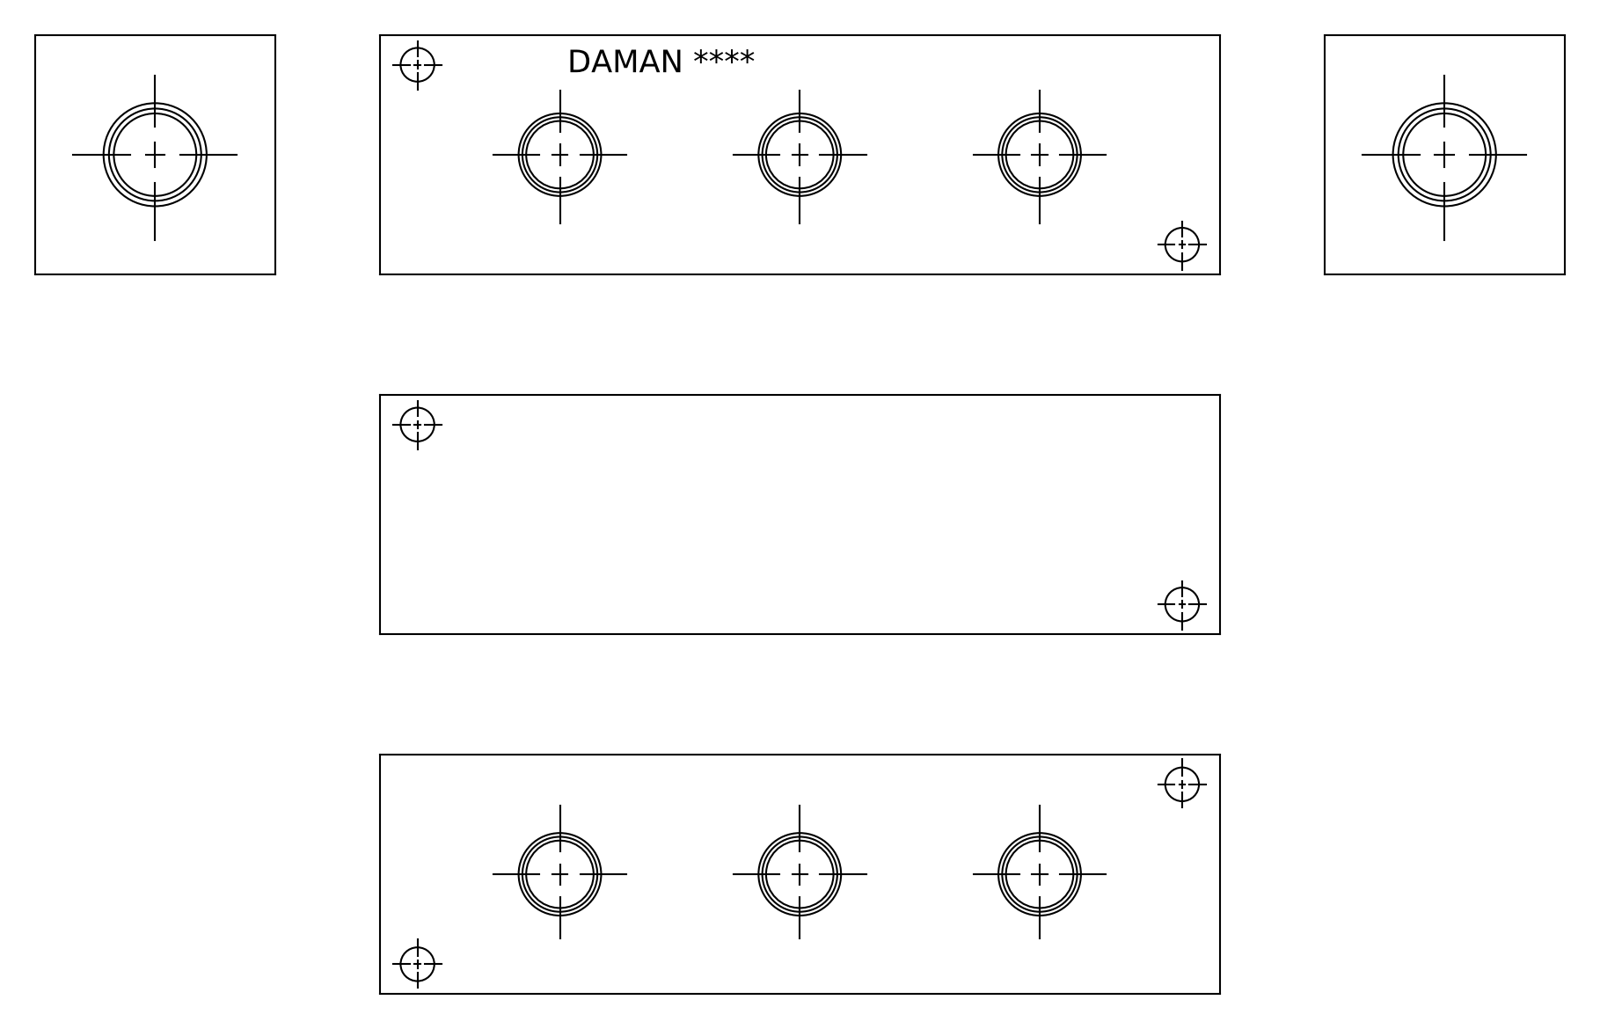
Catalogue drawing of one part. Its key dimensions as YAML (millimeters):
step_written_by: "Autodesk Inventor 2019 (AUTOMOTIVE_DESIGN)"
units: millimeters
bodies: {solids: 1, faces: 368, planar: 226, cylindrical: 24, other: 118}
overall_size: [177.8, 50.8, 50.8]
volume: 420508
surface_area: 51846
round_holes:
  - {diameter: 7.14, count: 4}
  - {diameter: 14.3, count: 3}
  - {diameter: 17.3, count: 3}
  - {diameter: 17.48, count: 1}
  - {diameter: 21.59, count: 1}
face_to_face_distances: [50.8, 177.8, 11.73, 39.07, 15.37, 162.43, 27.34, 147.06, 49.8, 38.07]
hole_center_spacings: [35.69, 50.8, 83.19, 133.15, 166.38, 101.6]
